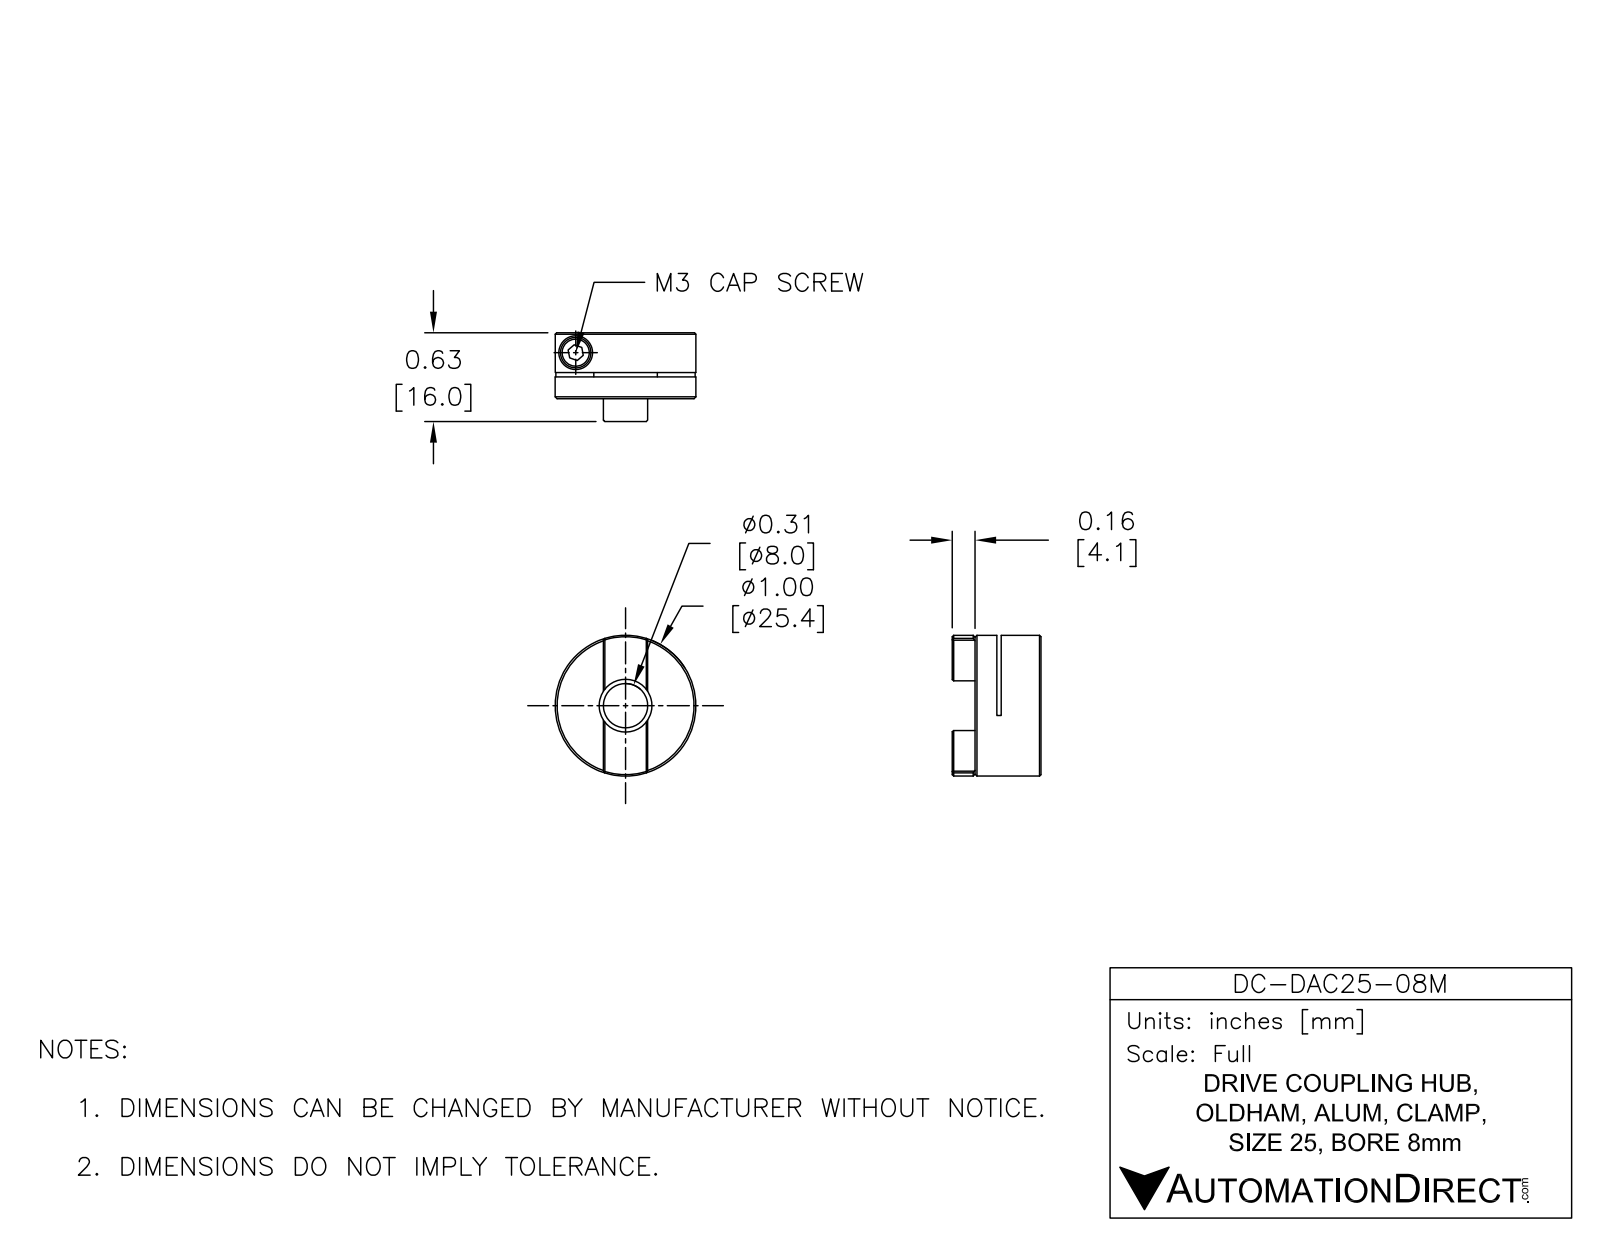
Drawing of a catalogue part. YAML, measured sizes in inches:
part_name: "DC-DAC25-08M"
step_written_by: "SolidWorks 2015 (AUTOMOTIVE_DESIGN)"
units: inches
bodies: {solids: 0, faces: 56, planar: 29, cylindrical: 17, other: 10}
overall_size: [1, 1, 0.63]
round_holes:
  - {diameter: 0.097, count: 1}
  - {diameter: 0.134, count: 1}
  - {diameter: 0.24, count: 1}
  - {diameter: 0.315, count: 1}
  - {diameter: 0.375, count: 1}
round_bosses_or_shafts:
  - {diameter: 1, count: 1}
face_to_face_distances: [0.468, 0.313, 0.155, 0.282, 0.031, 0.186, 0.63, 0.348, 0.317, 0.162]
